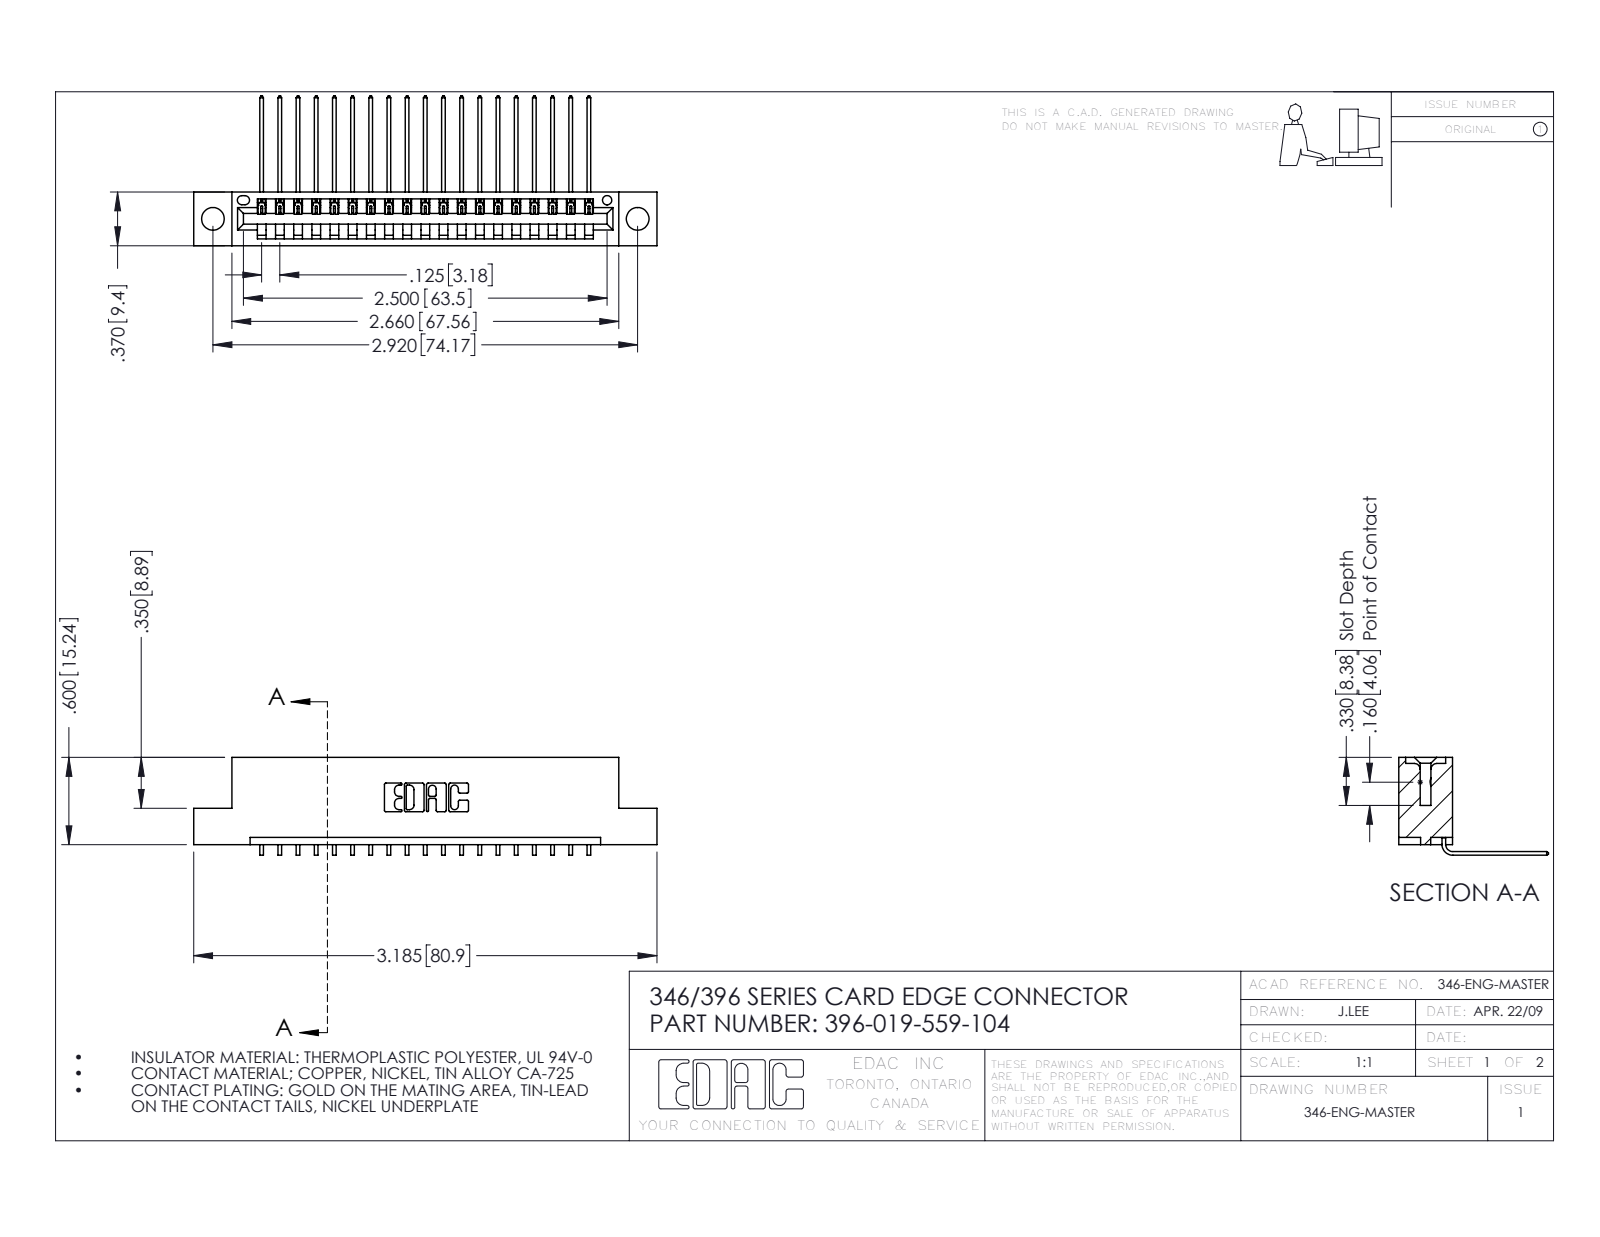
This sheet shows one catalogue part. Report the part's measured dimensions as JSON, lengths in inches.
{"part_name": "396-019-559-104; 345-292-001_558 559 Tail - 1; 346 Part_Flush Mounting Lugs - 0.156 Dia-TH", "step_written_by": "SolidWorks 2016 (CONFIG_CONTROL_DESIGN)", "units": "inches", "bodies": {"solids": 20, "faces": 1262, "planar": 874, "cylindrical": 388, "other": 0}, "overall_size": [3.185, 1.03, 0.673], "volume_in3": 0.461, "surface_area_in2": 14.55, "round_holes": [[0.156, 2], [0.064, 1]], "partial_cylinders_radius": [[0.006, 38], [0.01, 22], [0.007, 6], [0.031, 6], [0.026, 3], [0.031, 2], [0.04, 2], [0.014, 1]], "face_to_face_distances": [0.048, 0.322, 0.37, 0.25, 0.072, 0.025, 0.298, 0.148, 0.222, 0.1], "hole_center_spacings": [0.246, 2.713, 2.92]}
